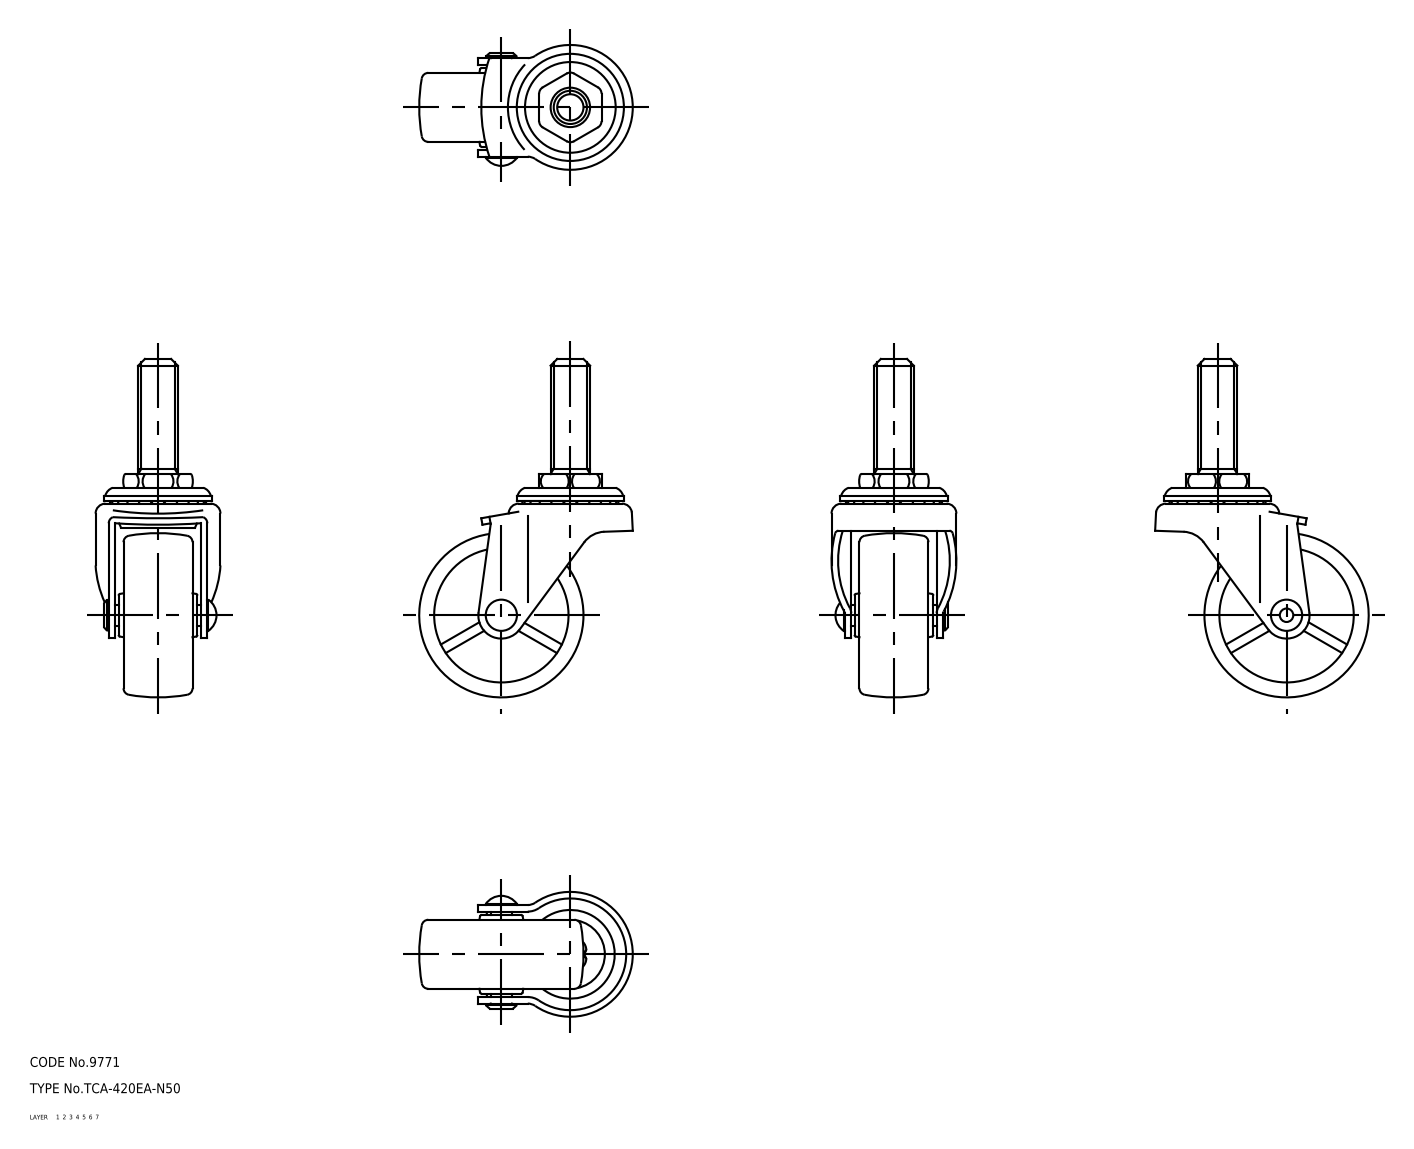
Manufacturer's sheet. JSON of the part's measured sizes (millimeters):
{"part_name": "wheel; mounting plate; main shaft; axle (+1 more)", "step_written_by": "CADfix (AUTOMOTIVE_DESIGN)", "units": "millimeters", "bodies": {"solids": 5, "faces": 323, "planar": 0, "cylindrical": 0, "other": 323}, "overall_size": [103, 65.41, 38], "volume_mm3": 47649, "surface_area_mm2": 22995}
